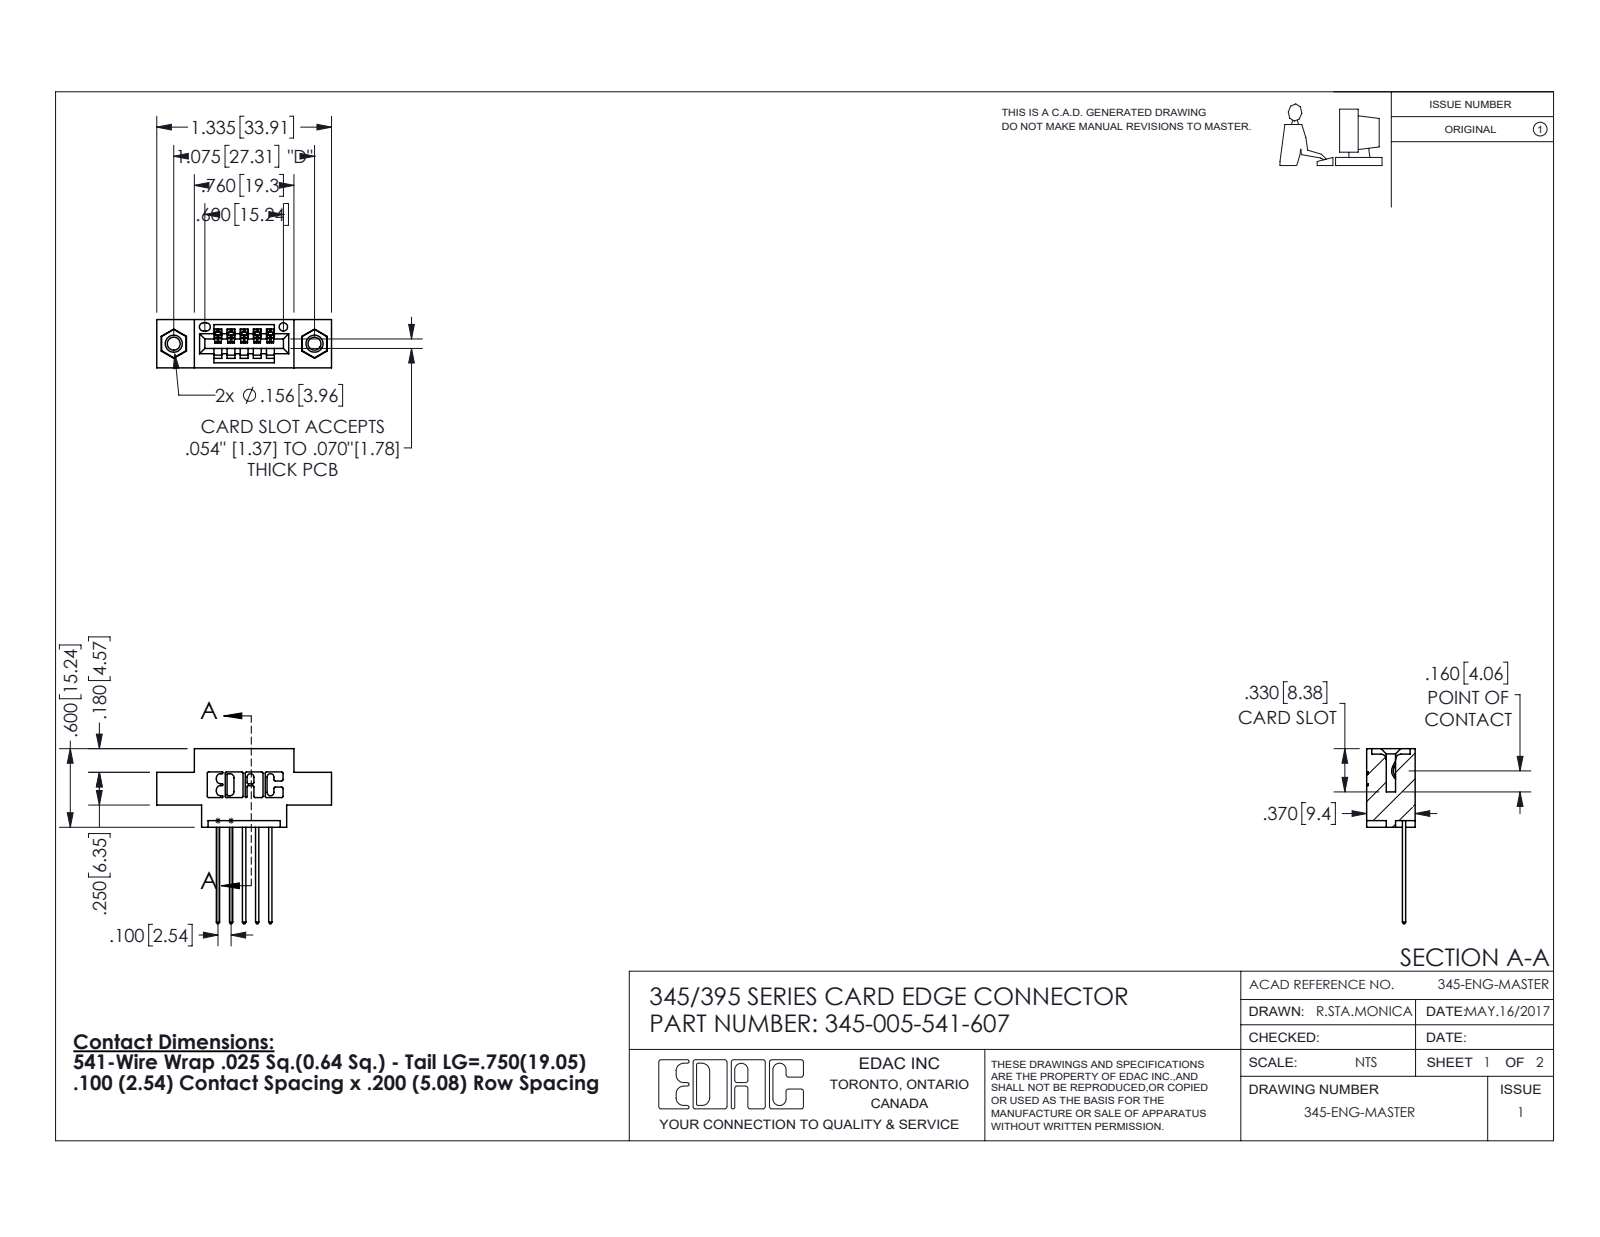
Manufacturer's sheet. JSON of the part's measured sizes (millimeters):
{"part_name": "345-292-001_345-293-141; 345-005-541-607; 345 Part_0.170 Offset - 0.156 Dia-TI; 345-250-001_345-250-005-103", "step_written_by": "SolidWorks 2016 (CONFIG_CONTROL_DESIGN)", "units": "millimeters", "bodies": {"solids": 8, "faces": 480, "planar": 316, "cylindrical": 148, "other": 16}, "overall_size": [34, 33.9, 9.4], "volume_mm3": 2800, "surface_area_mm2": 3484, "round_holes": [[2.5, 2], [3.2, 2], [4, 2], [1.6, 1]], "round_bosses_or_shafts": [[3.9, 2]], "partial_cylinders_radius": [[0.3, 22], [0.2, 10], [0.3, 10], [0.2, 6], [0.8, 6], [0.7, 3], [0.8, 2], [1, 2]], "face_to_face_distances": [9.4, 5.1, 1.8, 7.6, 2.5, 0.6, 2.5, 6.9, 6.4, 1.5], "hole_center_spacings": [6.9, 21.5, 27.3]}
